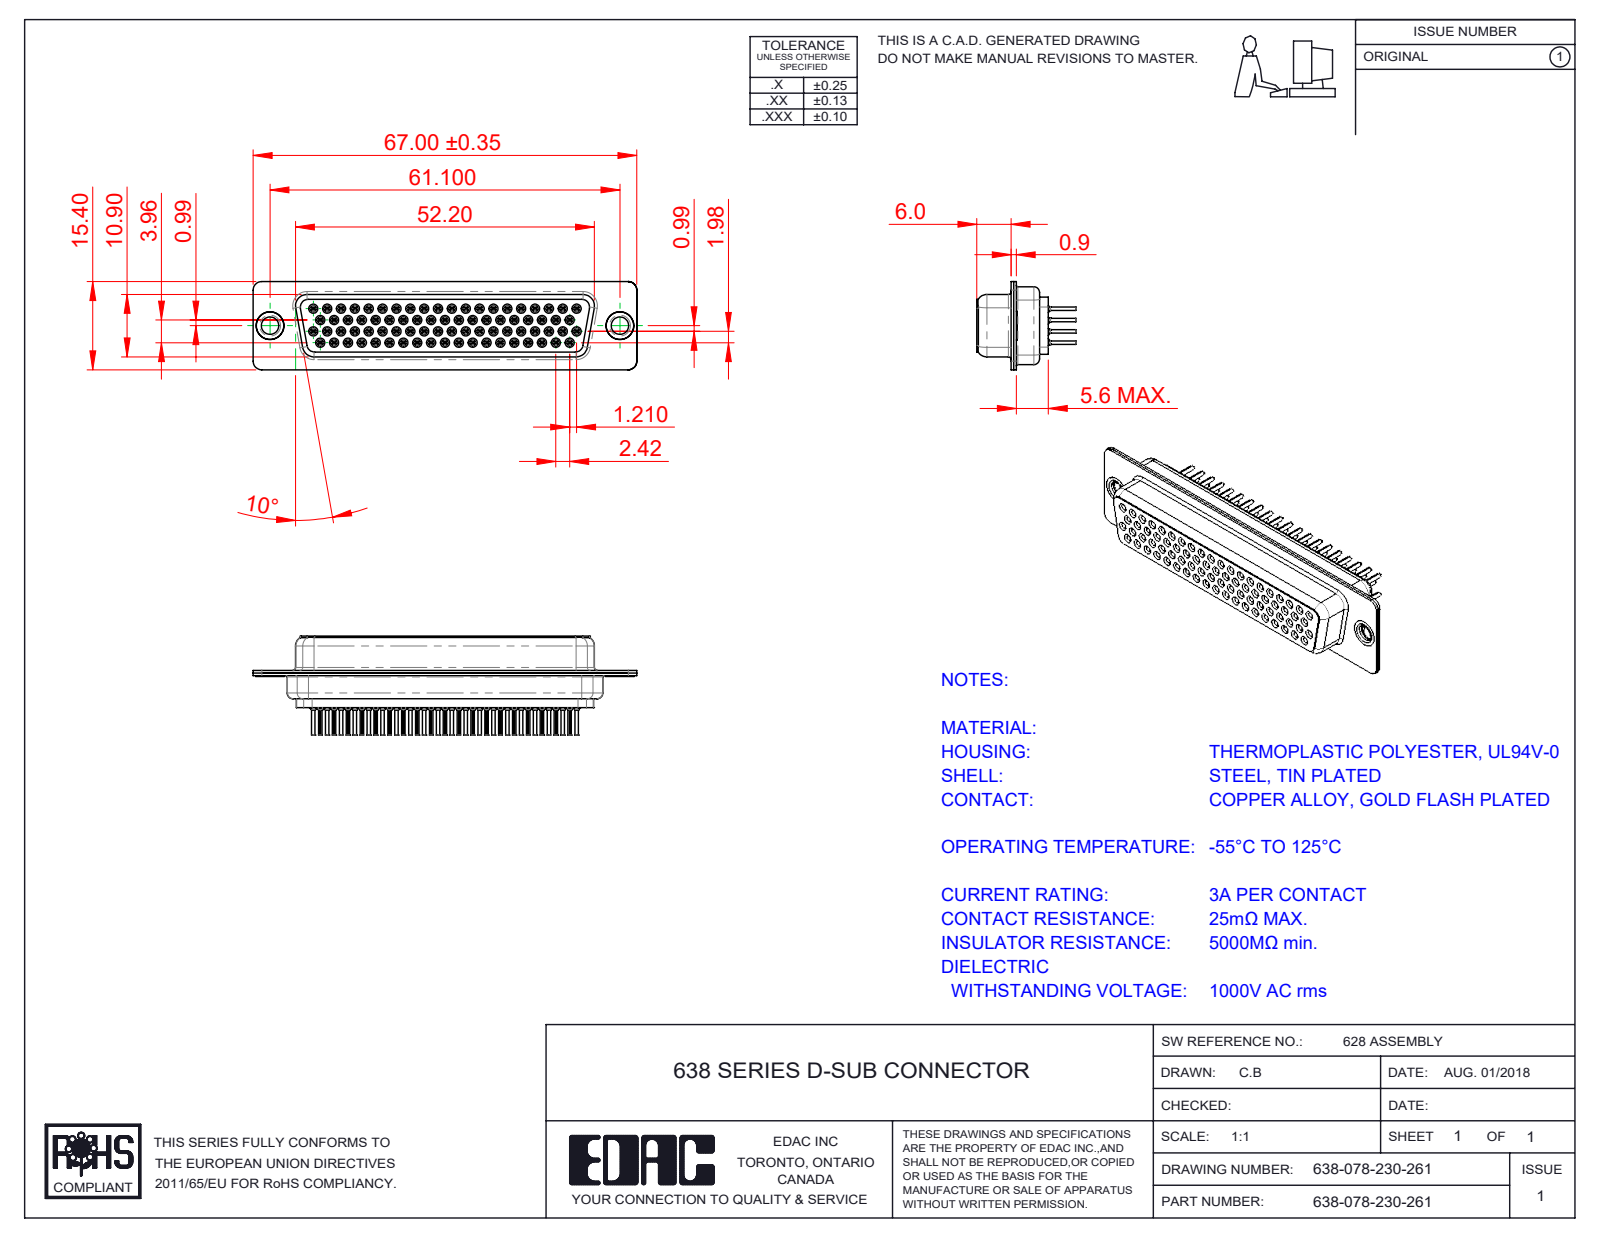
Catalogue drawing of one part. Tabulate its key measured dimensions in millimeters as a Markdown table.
| quantity | value |
| --- | --- |
| part name | 638 Contact Row 1_30; 638 Contact Row 3_30; 638 Thru Hole Rivet; 638 Shell Rear_78 Contacts (+5 more) |
| STEP written by | SolidWorks 2020 (CONFIG_CONTROL_DESIGN) |
| units | millimeters |
| bodies | 83 solids, 10159 faces (2485 planar, 2695 cylindrical, 4979 other) |
| overall size | 67 × 17.3 × 15.4 |
| volume | 5 797 mm³ |
| surface area | 20 378 mm² |
| round holes (diameter × count) | 0.2 × 78, 0.8 × 78, 1 × 78, 1.1 × 78, 1.6 × 78, 1.7 × 78, 1.8 × 78, 3.05 × 2, 4 × 2, 4.05 × 2, 4.85 × 2 |
| round bosses / shafts (diameter × count) | 2 × 78, 1.5 × 78, 1.2 × 78, 0.6 × 78, 5 × 2, 4.95 × 2, 4.8 × 2, 3.55 × 2 |
| partial cylindrical surfaces (radius × count) | 0.1 × 156, 0.28 × 39, 1.5 × 16, 2 × 12, 1.55 × 8, 0.25 × 4, 0.5 × 4, 0.55 × 4 |
| main face-to-face distances | 0.45, 0.4, 0.9, 1.35, 9.6, 11.8, 1.8, 11.4, 2.2, 13.15 |
| hole center spacings | 2.42, 4.84, 7.26, 9.68, 6.06, 12.1, 6.96, 8.48 |
